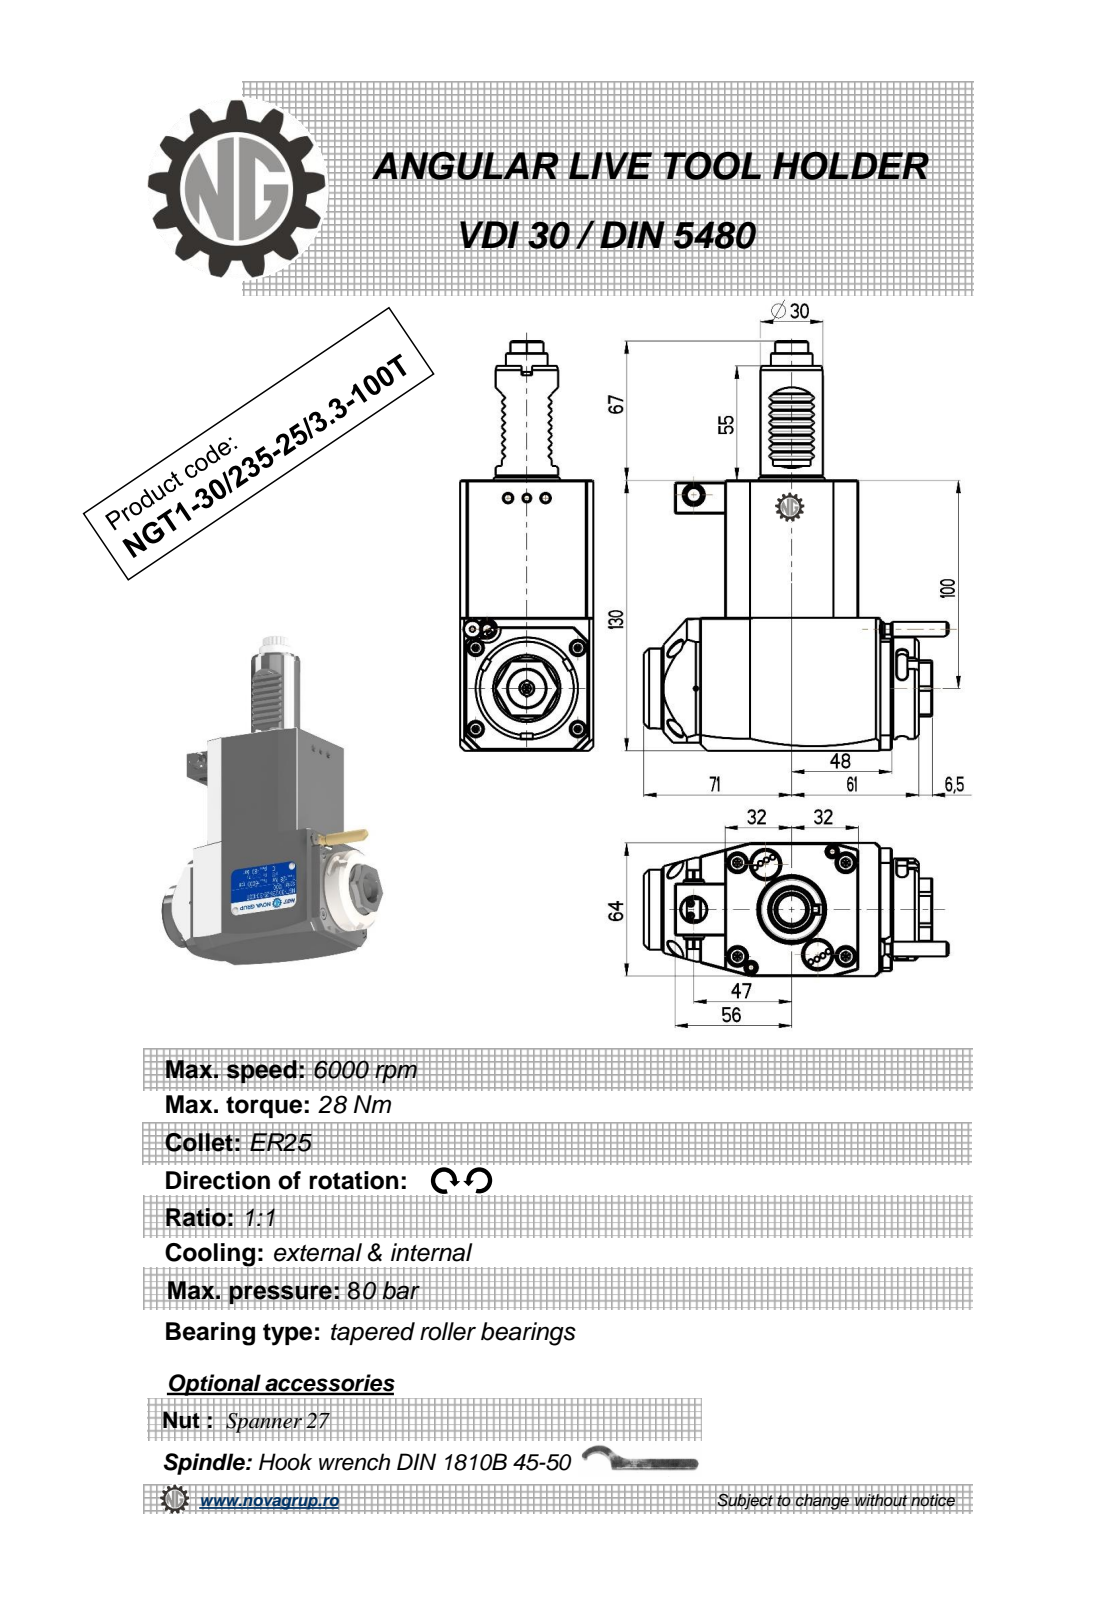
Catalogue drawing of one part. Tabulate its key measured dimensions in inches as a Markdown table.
| quantity | value |
| --- | --- |
| part name | NGT1_30_235_25_3_3_100T |
| STEP written by | PRO/ENGINEER BY PARAMETRIC TECHNOLOGY CORPORATION, 2010280 (CONFIG_CONTROL_DESIGN) |
| units | inches |
| bodies | 1 solid, 472 faces (217 planar, 163 cylindrical, 92 other) |
| overall size | 7.756 × 5.763 × 2.52 |
| volume | 45.7 in³ |
| surface area | 97.84 in² |
| round holes (diameter × count) | 0.098 × 1, 0.118 × 1, 0.374 × 1, 0.472 × 1, 0.709 × 1 |
| round bosses / shafts (diameter × count) | 0.315 × 2, 1.929 × 1, 1.654 × 1, 1.516 × 1, 1.181 × 1, 0.787 × 1, 0.394 × 1, 0.276 × 1 |
| partial cylindrical surfaces (radius × count) | 0.078 × 36, 0.012 × 16, 0.098 × 6, 7.087 × 2, 0.152 × 1, 0.167 × 1, 0.177 × 1, 0.279 × 1 |
| main face-to-face distances | 2.52, 5.118, 0.63, 3.15, 2.842, 0.512, 2.598, 3.661, 1.142, 0.111 |
| hole center spacings | 1.348, 2.591, 3.602 |
